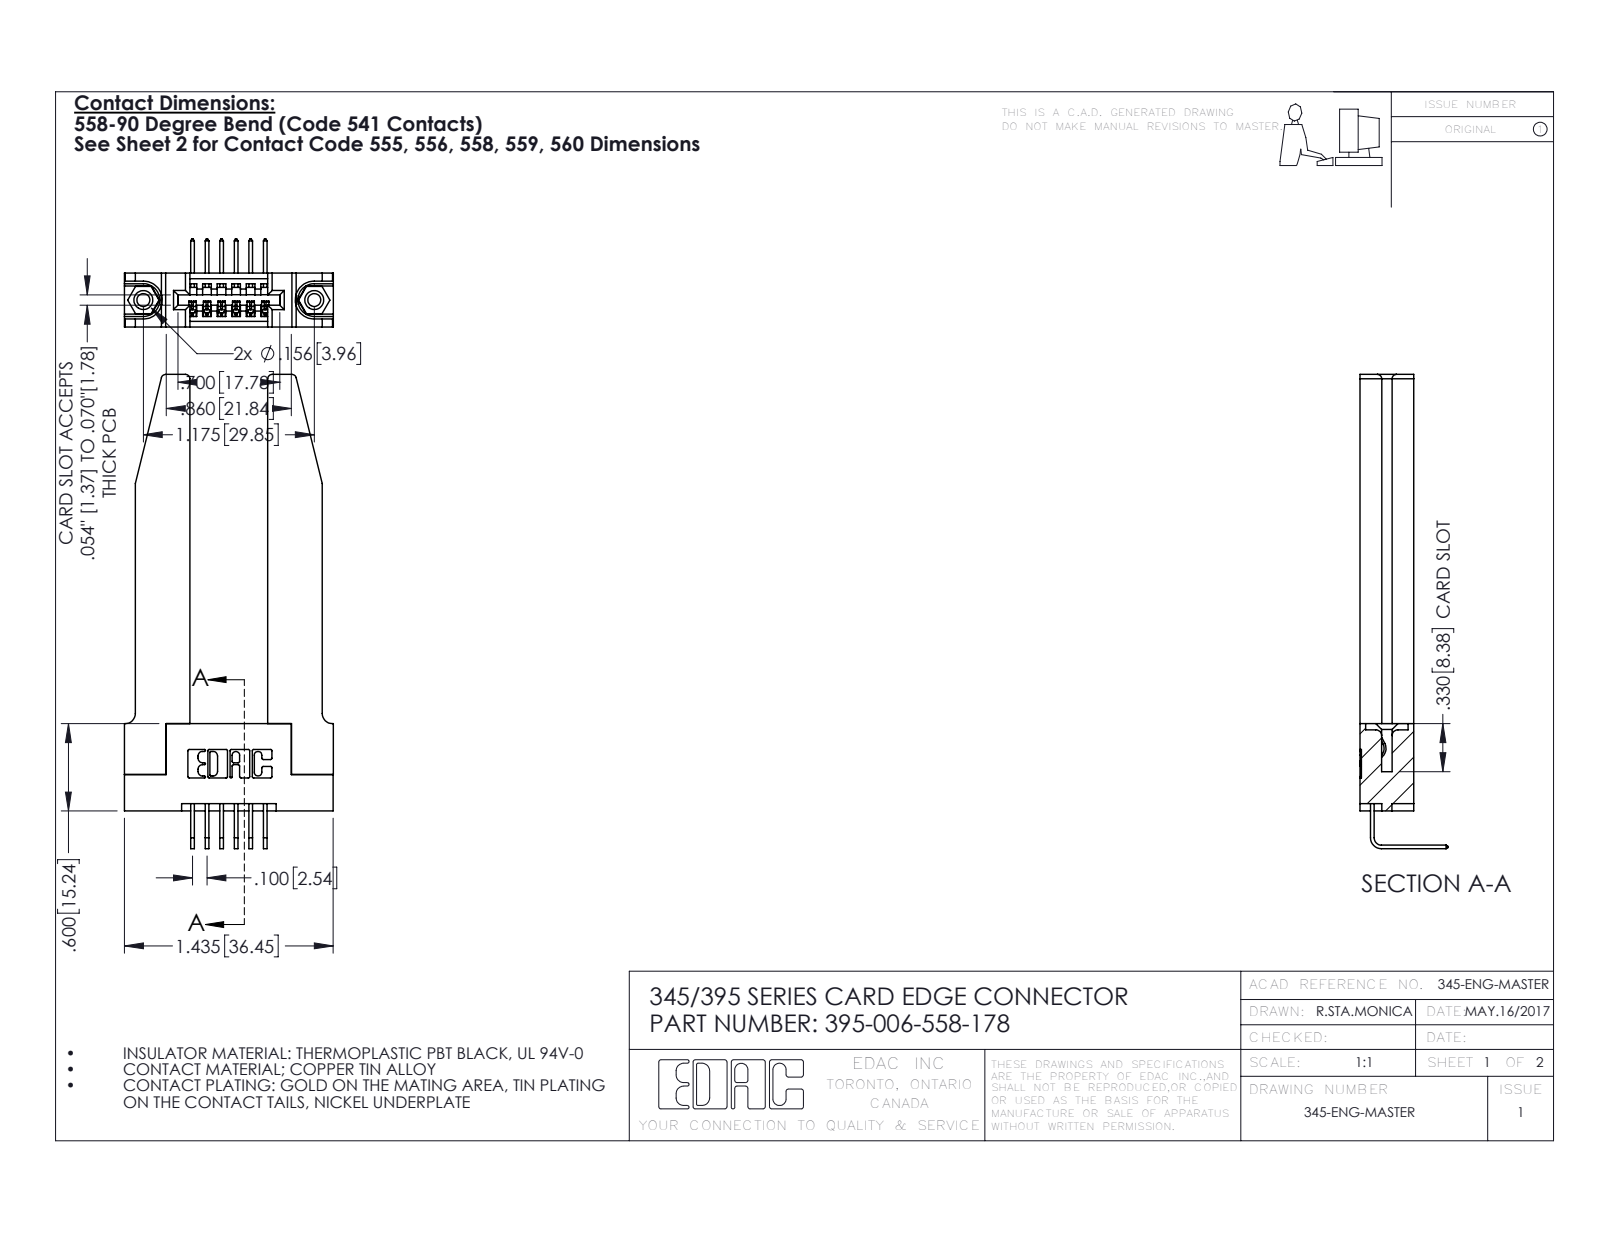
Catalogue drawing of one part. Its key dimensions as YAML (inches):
part_name: "345-220-078_345-220-078; 395-006-558-178; 345-250-001_345-250-001-102; 345-292-001_558 Tail - 2 (+1 more)"
step_written_by: "SolidWorks 2016 (CONFIG_CONTROL_DESIGN)"
units: inches
bodies: {solids: 11, faces: 720, planar: 474, cylindrical: 194, other: 52}
overall_size: [3.259, 1.436, 0.605]
volume: 0.669
surface_area: 16.6
round_holes:
  - {diameter: 0.089, count: 2}
  - {diameter: 0.125, count: 2}
  - {diameter: 0.156, count: 2}
  - {diameter: 0.064, count: 1}
round_bosses_or_shafts:
  - {diameter: 0.155, count: 2}
partial_cylinders:
  - {radius: 0.01, count: 22}
  - {radius: 0.006, count: 12}
  - {radius: 0.03, count: 8}
  - {radius: 0.007, count: 6}
  - {radius: 0.031, count: 6}
  - {radius: 0.026, count: 3}
  - {radius: 0.031, count: 2}
  - {radius: 0.04, count: 2}
face_to_face_distances: [0.37, 0.15, 0.22, 0.535, 0.072, 0.148, 0.077, 0.298, 0.2, 0.095]
hole_center_spacings: [0.27, 0.946, 1.175]
